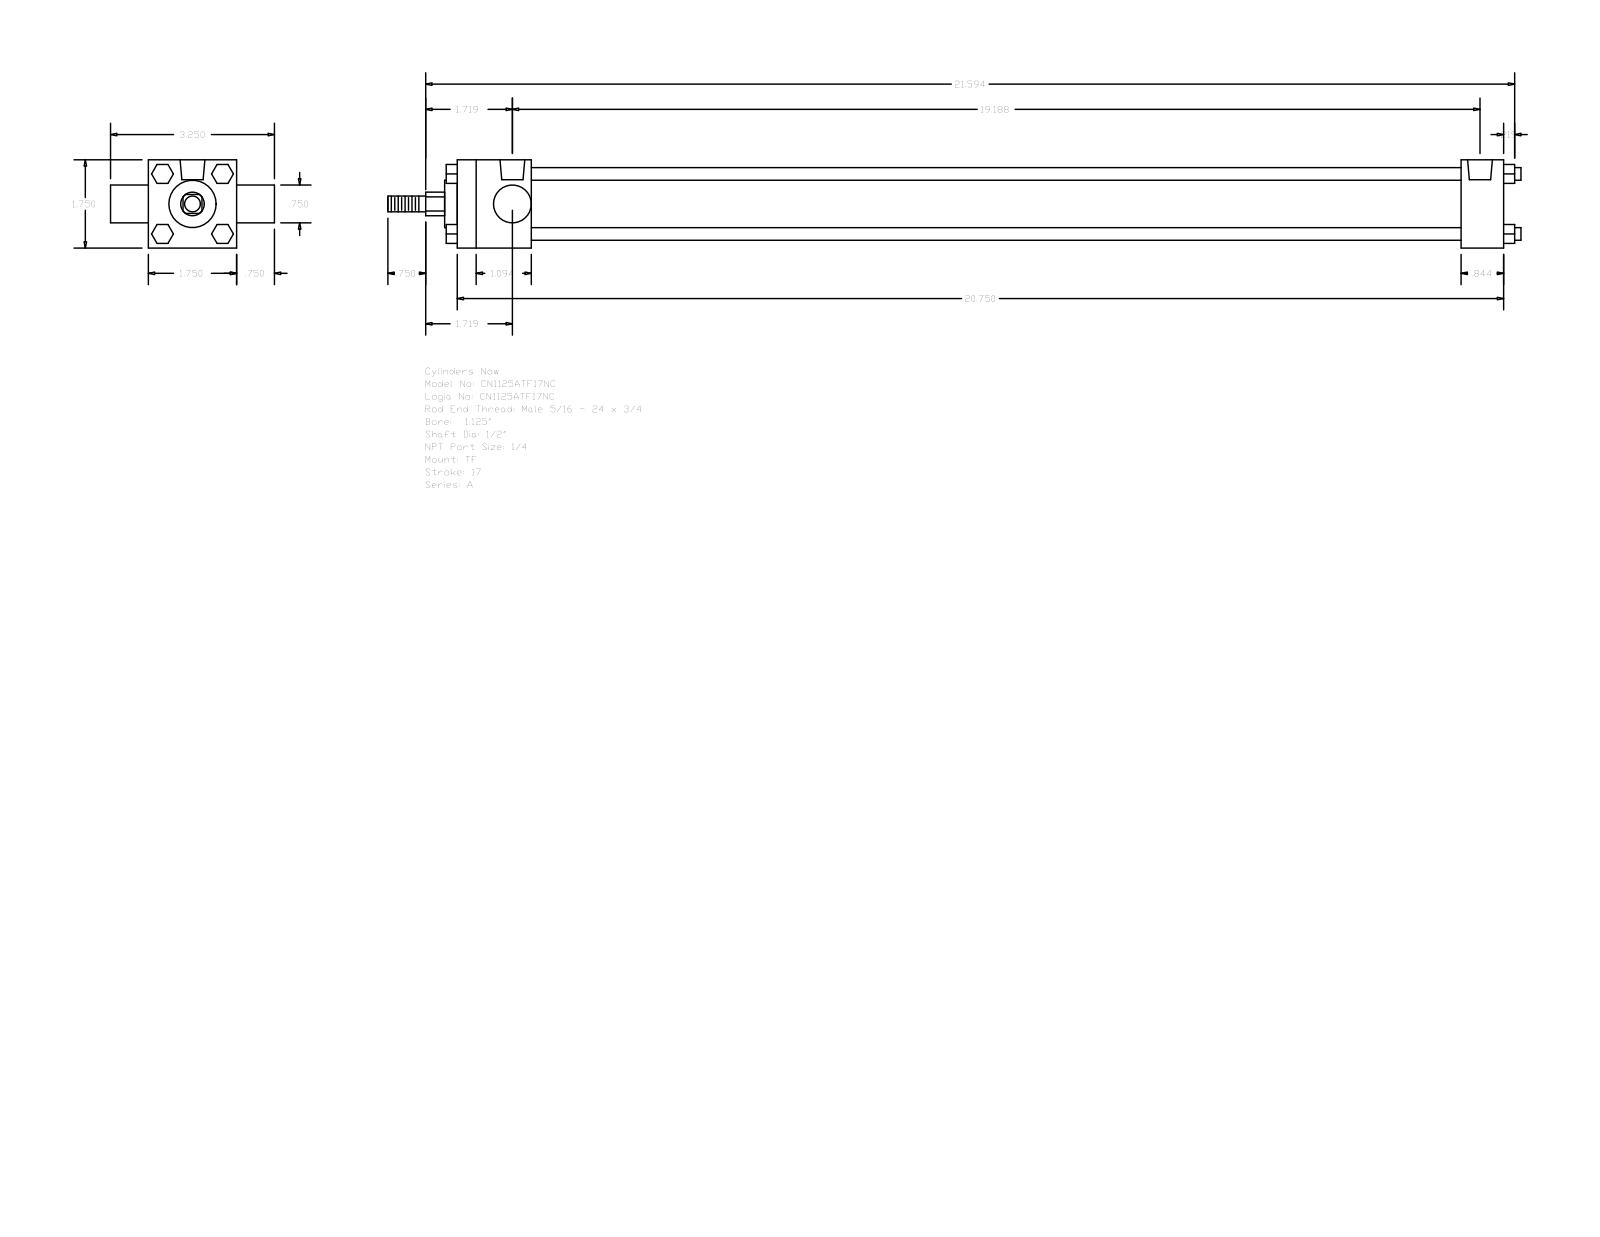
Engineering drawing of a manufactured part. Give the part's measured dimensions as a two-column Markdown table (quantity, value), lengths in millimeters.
| quantity | value |
| --- | --- |
| part name | A_TF__0112_0.5 |
| STEP written by | GSSL Pune (CONFIG_CONTROL_DESIGN) |
| units | millimeters |
| bodies | 0 solids, 120 faces (92 planar, 28 cylindrical, 0 other) |
| overall size | 570.71 × 82.55 × 44.45 |
| round holes (diameter × count) | 5.56 × 3, 12.49 × 2 |
| round bosses / shafts (diameter × count) | 6.35 × 4, 31.88 × 1, 23.81 × 1, 19.05 × 1, 12.7 × 1, 7.94 × 1 |
| partial cylindrical surfaces (radius × count) | 5.94 × 1 |
| main face-to-face distances | 44.46, 527.04, 505.61, 21.43, 37.3, 468.31, 489.74, 19.04, 63.5, 9.53 |
| hole center spacings | 1.58, 1.59, 484.19, 485.77, 485.78, 487.36 |
